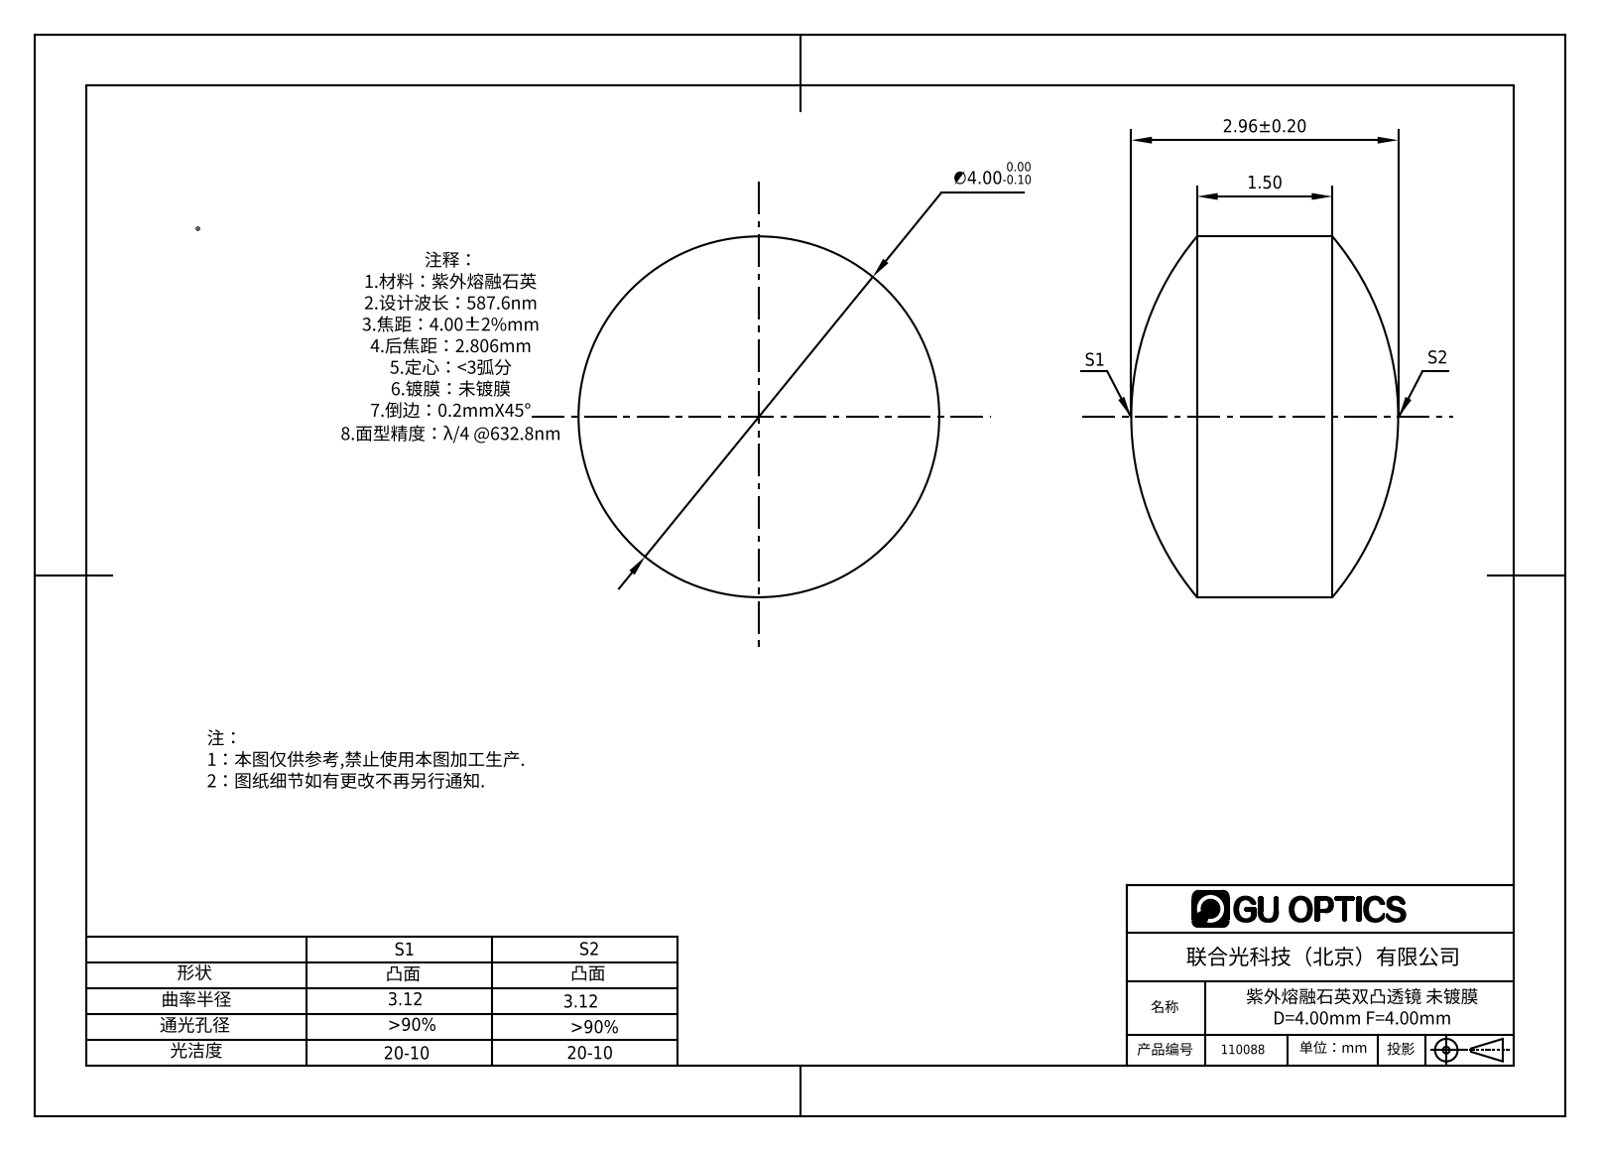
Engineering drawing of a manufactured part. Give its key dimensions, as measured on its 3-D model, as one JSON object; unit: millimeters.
{"part_name": "110088", "step_written_by": "SolidWorks 2016 (CONFIG_CONTROL_DESIGN)", "units": "millimeters", "bodies": {"solids": 1, "faces": 6, "planar": 0, "cylindrical": 2, "other": 4}, "overall_size": [4, 4, 2.96], "volume_mm3": 28, "surface_area_mm2": 47, "round_bosses_or_shafts": [[4, 1]]}
